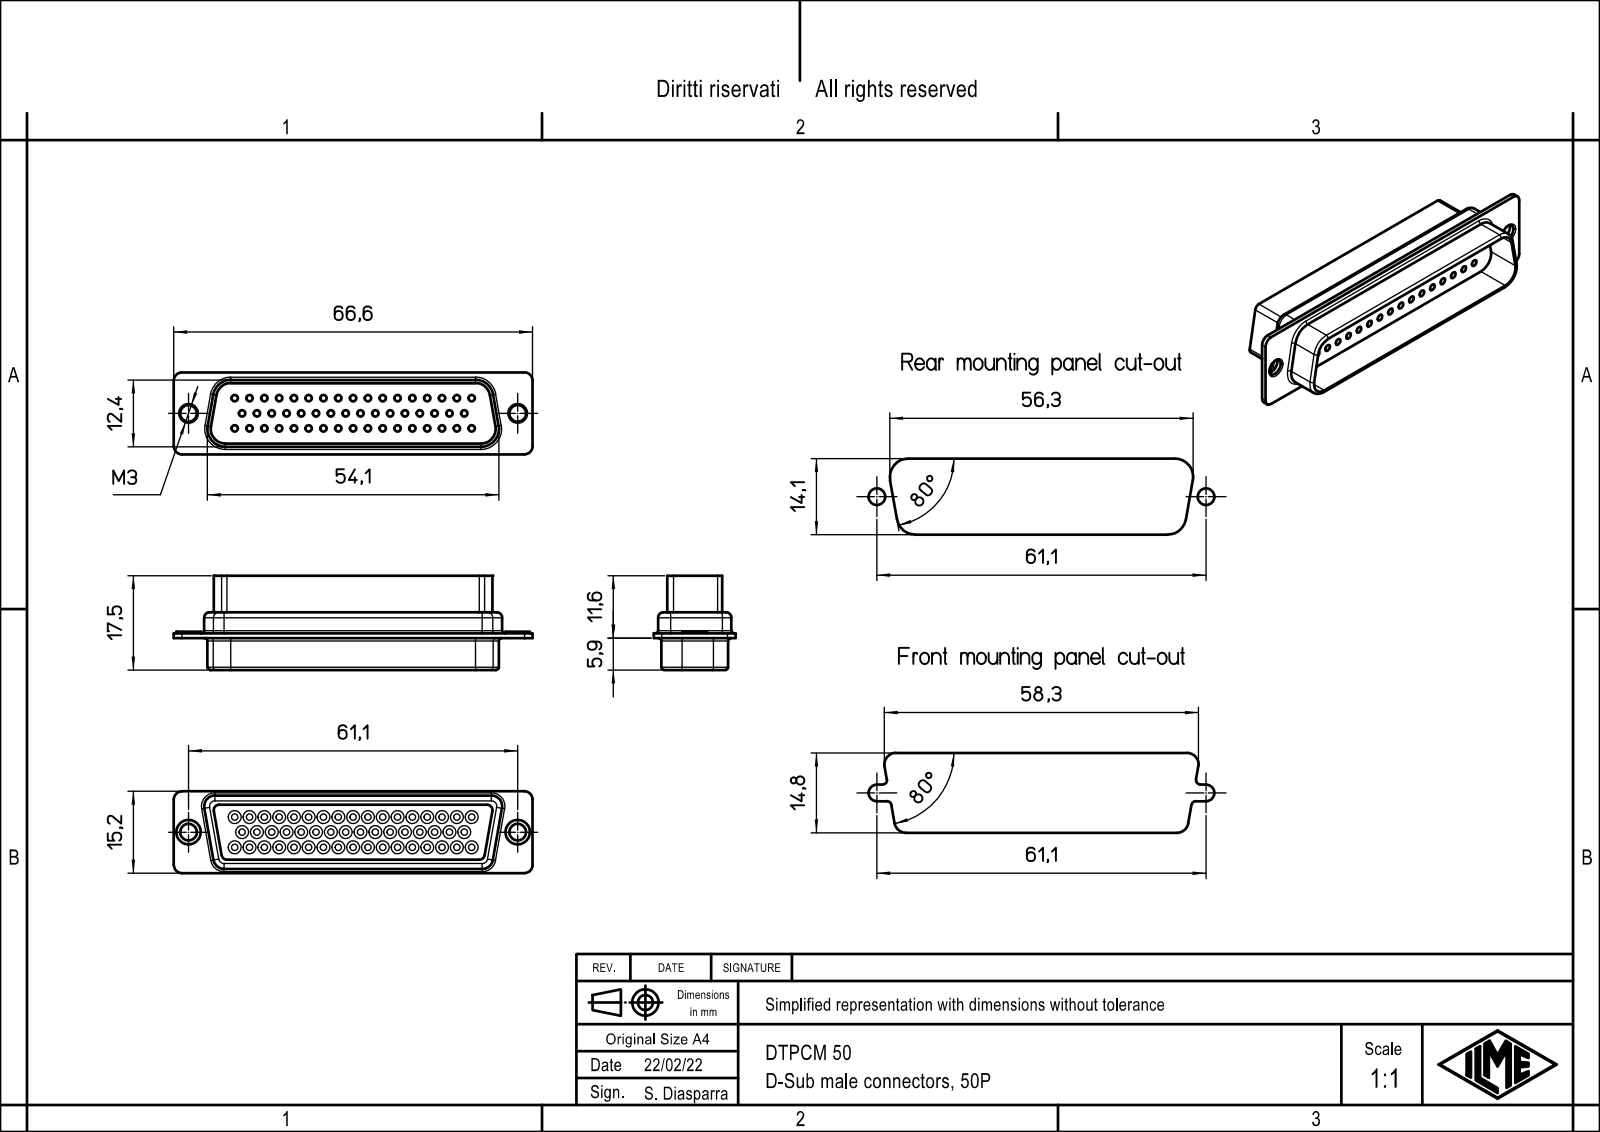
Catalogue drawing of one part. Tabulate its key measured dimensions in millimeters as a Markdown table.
| quantity | value |
| --- | --- |
| part name | DPTCM_50 |
| STEP written by | Creo Elements/Direct Modeling 20.1B 02-Apr-2019 (C) Parametric Technology GmbH (AUTOMOTIVE_DESIGN) |
| units | millimeters |
| bodies | 1 solid, 342 faces (78 planar, 244 cylindrical, 20 other) |
| overall size | 66.6 × 17.5 × 15.2 |
| volume | 5 005 mm³ |
| surface area | 8 753 mm² |
| round holes (diameter × count) | 1.2 × 50, 2.4 × 50, 3.1 × 2 |
| round bosses / shafts (diameter × count) | 4.55 × 2 |
| partial cylindrical surfaces (radius × count) | 0.5 × 12, 1 × 8, 1.5 × 4, 2 × 4, 2.7 × 4, 3.3 × 4 |
| main face-to-face distances | 0.6, 0.5, 10.7, 12.4, 1.1, 11.3, 11.8, 10.2, 11.2, 11.1 |
| hole center spacings | 3.12, 2.75, 5.5, 11, 8.25, 13.75, 6.24, 7.85 |
